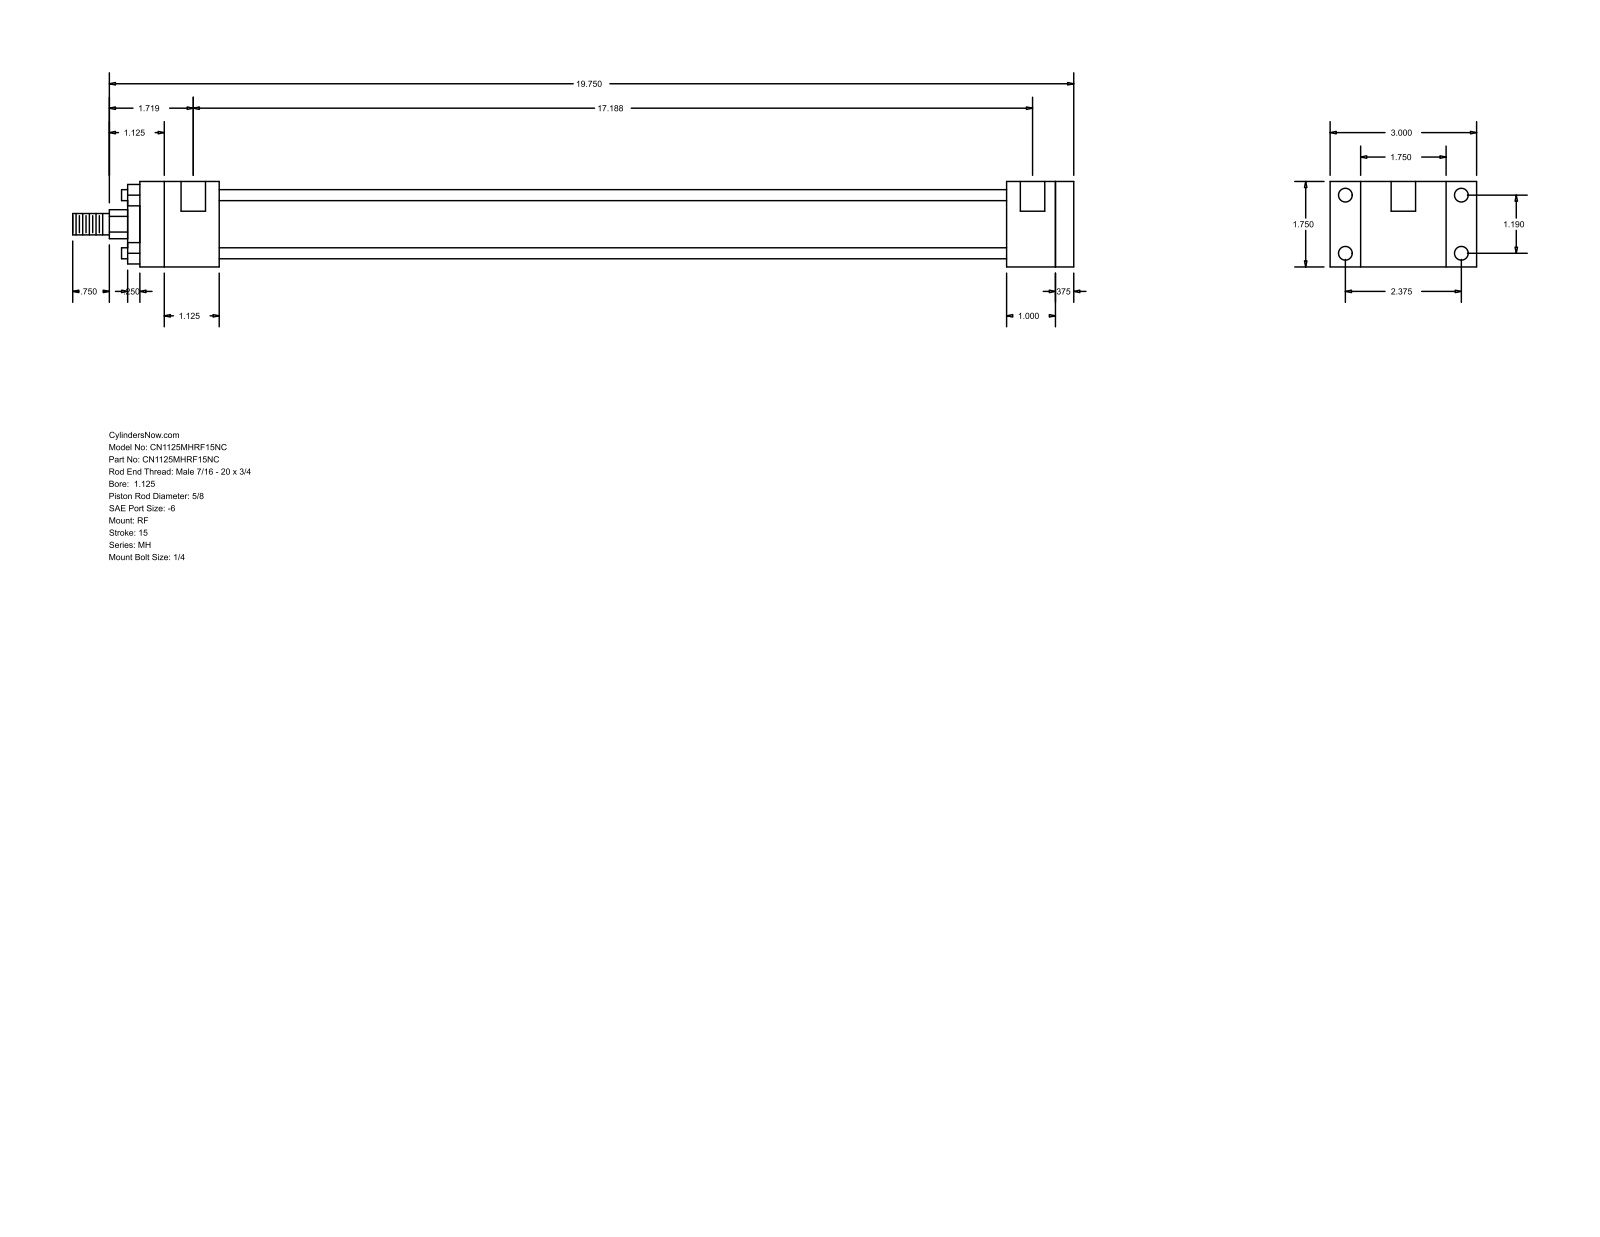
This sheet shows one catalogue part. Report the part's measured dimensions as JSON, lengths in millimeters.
{"part_name": "MH_RF__0112_0.625", "step_written_by": "GSSL Pune (CONFIG_CONTROL_DESIGN)", "units": "millimeters", "bodies": {"solids": 0, "faces": 92, "planar": 64, "cylindrical": 28, "other": 0}, "overall_size": [520.7, 76.2, 44.45], "round_holes": [[5.56, 4], [7.14, 4], [12.7, 2]], "round_bosses_or_shafts": [[5.71, 4], [34.92, 1], [28.57, 1], [15.88, 1], [11.11, 1]], "partial_cylinders_radius": [[7.54, 1]], "face_to_face_distances": [44.46, 9.53, 485.77, 15.87, 434.97, 444.5, 409.58, 25.39, 34.92, 41.27], "hole_center_spacings": [30.22, 60.32, 67.47, 433.39, 3.17, 436.56]}
